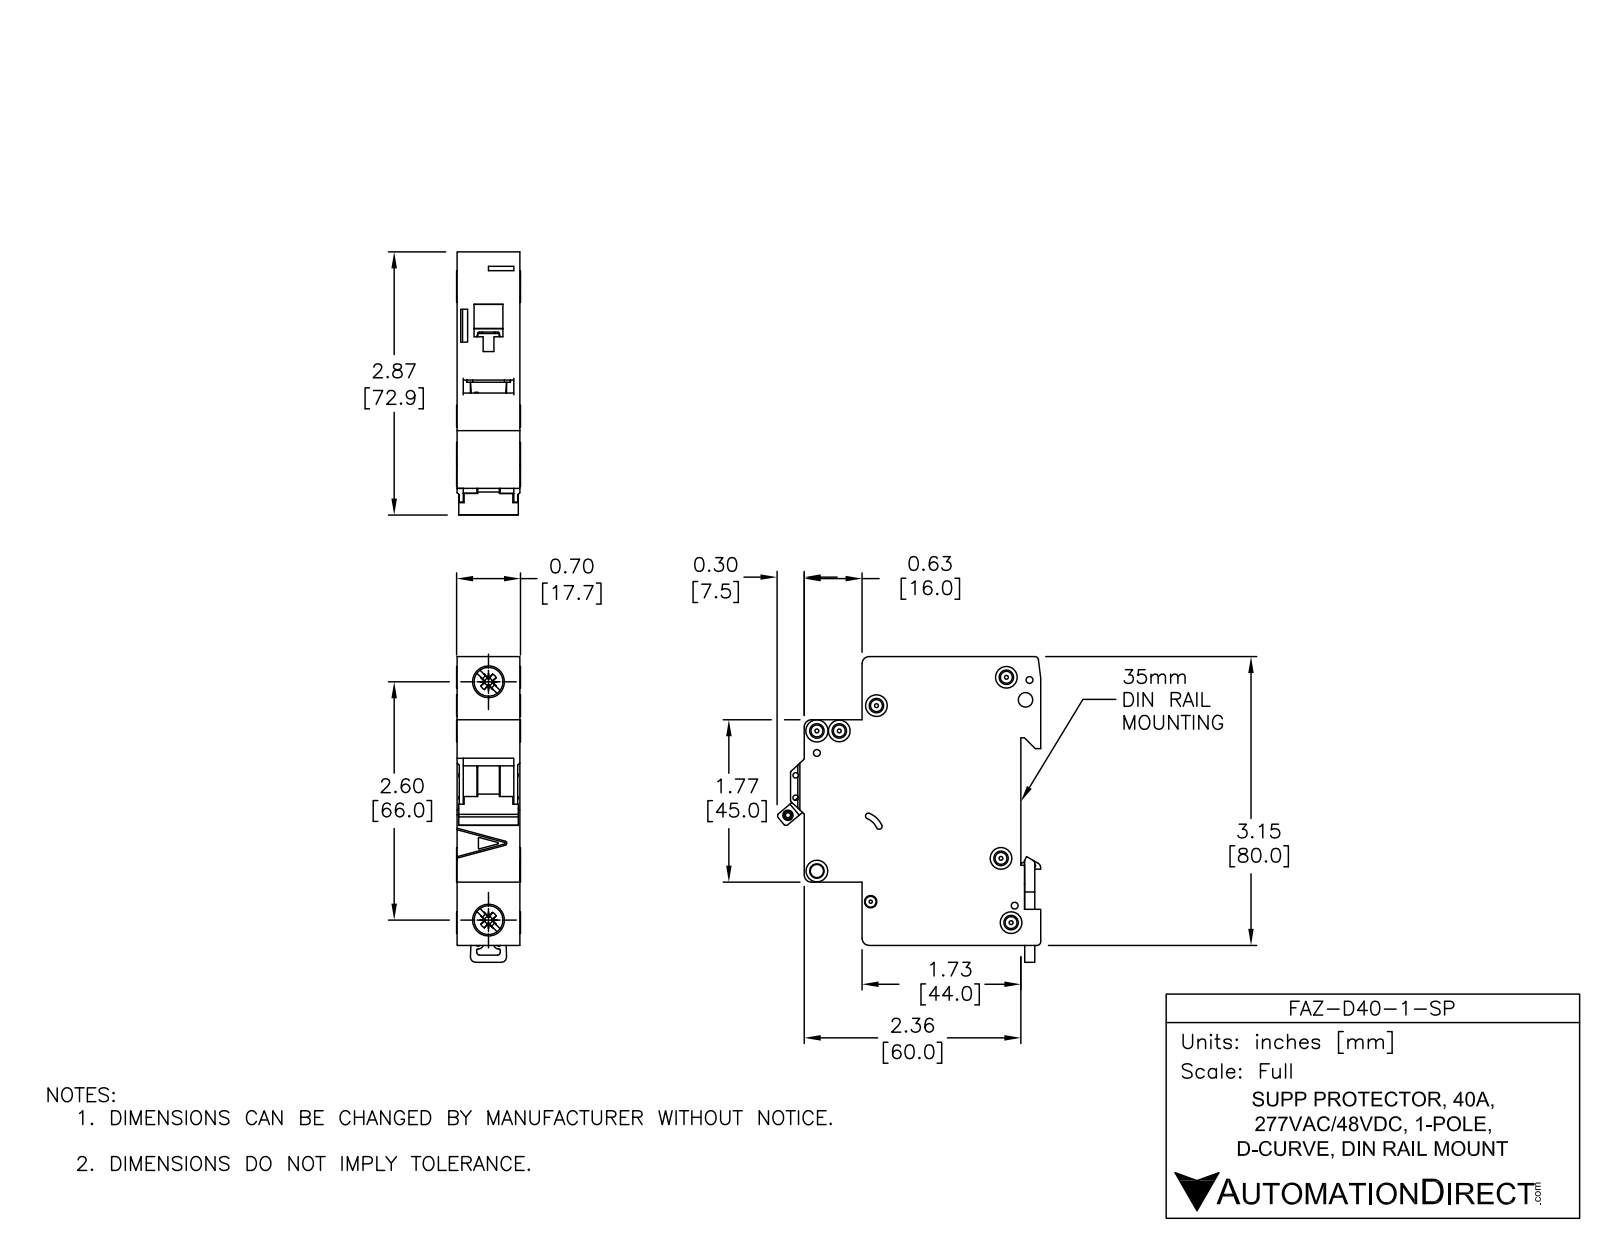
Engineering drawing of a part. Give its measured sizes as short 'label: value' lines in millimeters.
name: FAZ-D40-1-SP
written by: SolidWorks 2014 (AUTOMOTIVE_DESIGN)
unit: mm
bodies: 5 solids, 558 faces (235 planar, 202 cylindrical, 121 other)
size: 84.78 × 73.04 × 17.7
volume: 74 935 mm³; area: 19 545 mm²
holes: 6× ⌀3.6, 3× ⌀1.9, 2× ⌀1.09, 2× ⌀1.5, 2× ⌀4, 2× ⌀7.15, 1× ⌀2.15, 1× ⌀2.2, 1× ⌀2.55, 1× ⌀3.3, 1× ⌀3.4
bosses: 4× ⌀6, 2× ⌀8.2, 1× ⌀2.5
rounds: 30× R0.25, 13× R0.5, 8× R2, 5× R0.2, 4× R1, 2× R0.8, 2× R3, 1× R1.5
face distances: 17.5, 79.48, 5.5, 49.5, 44, 65.5, 60, 16, 1.75, 15.75
hole spacings: 6.2, 13.64, 4.81, 5.19, 5.61, 6.1, 6.44, 8.19
